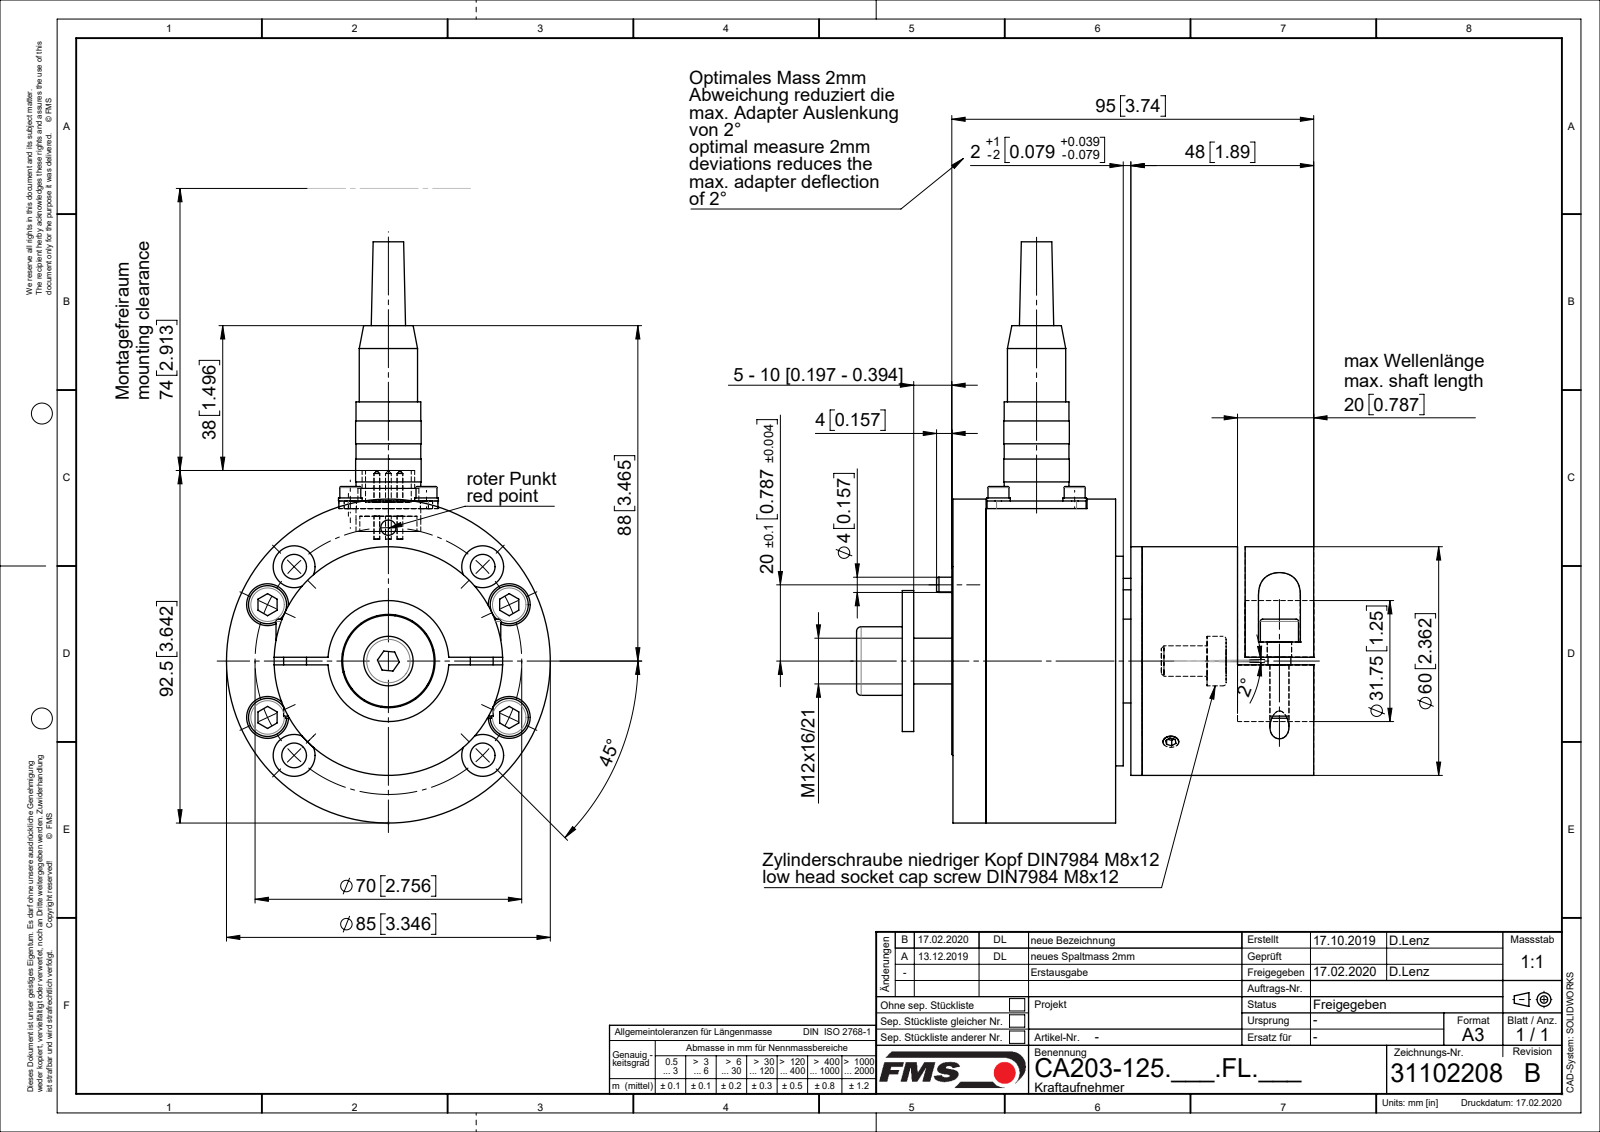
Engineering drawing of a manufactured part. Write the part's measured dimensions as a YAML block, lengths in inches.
part_name: "C0709101_DI125; C0709081; C0612056; C0709072 (+8 more)"
step_written_by: "Mechanical Desktop 2009 (CONFIG_CONTROL_DESIGN)"
units: inches
bodies: {solids: 37, faces: 671, planar: 221, cylindrical: 310, other: 140}
overall_size: [6.004, 4.744, 3.346]
volume: 19.26
surface_area: 171.1
round_holes:
  - {diameter: 0.102, count: 8}
  - {diameter: 0.256, count: 8}
  - {diameter: 0.433, count: 8}
  - {diameter: 0.203, count: 6}
  - {diameter: 0.126, count: 4}
  - {diameter: 0.142, count: 4}
  - {diameter: 0.157, count: 4}
  - {diameter: 0.276, count: 4}
  - {diameter: 0.252, count: 2}
  - {diameter: 0.118, count: 1}
  - {diameter: 0.17, count: 1}
  - {diameter: 0.281, count: 1}
round_bosses_or_shafts:
  - {diameter: 0.236, count: 10}
  - {diameter: 0.118, count: 8}
  - {diameter: 0.394, count: 6}
  - {diameter: 0.059, count: 5}
  - {diameter: 0.244, count: 4}
  - {diameter: 0.217, count: 4}
  - {diameter: 0.197, count: 4}
  - {diameter: 3.346, count: 1}
partial_cylinders:
  - {radius: 0.098, count: 4}
  - {radius: 0.197, count: 2}
  - {radius: 0.217, count: 2}
face_to_face_distances: [1.772, 1.949, 0.079, 0.354, 0.453, 1.24, 1.693, 0.394, 0.059, 1.594]
hole_center_spacings: [0.787, 0.976, 0.992, 1.291, 1.378, 2.013, 2.223, 1.113]
